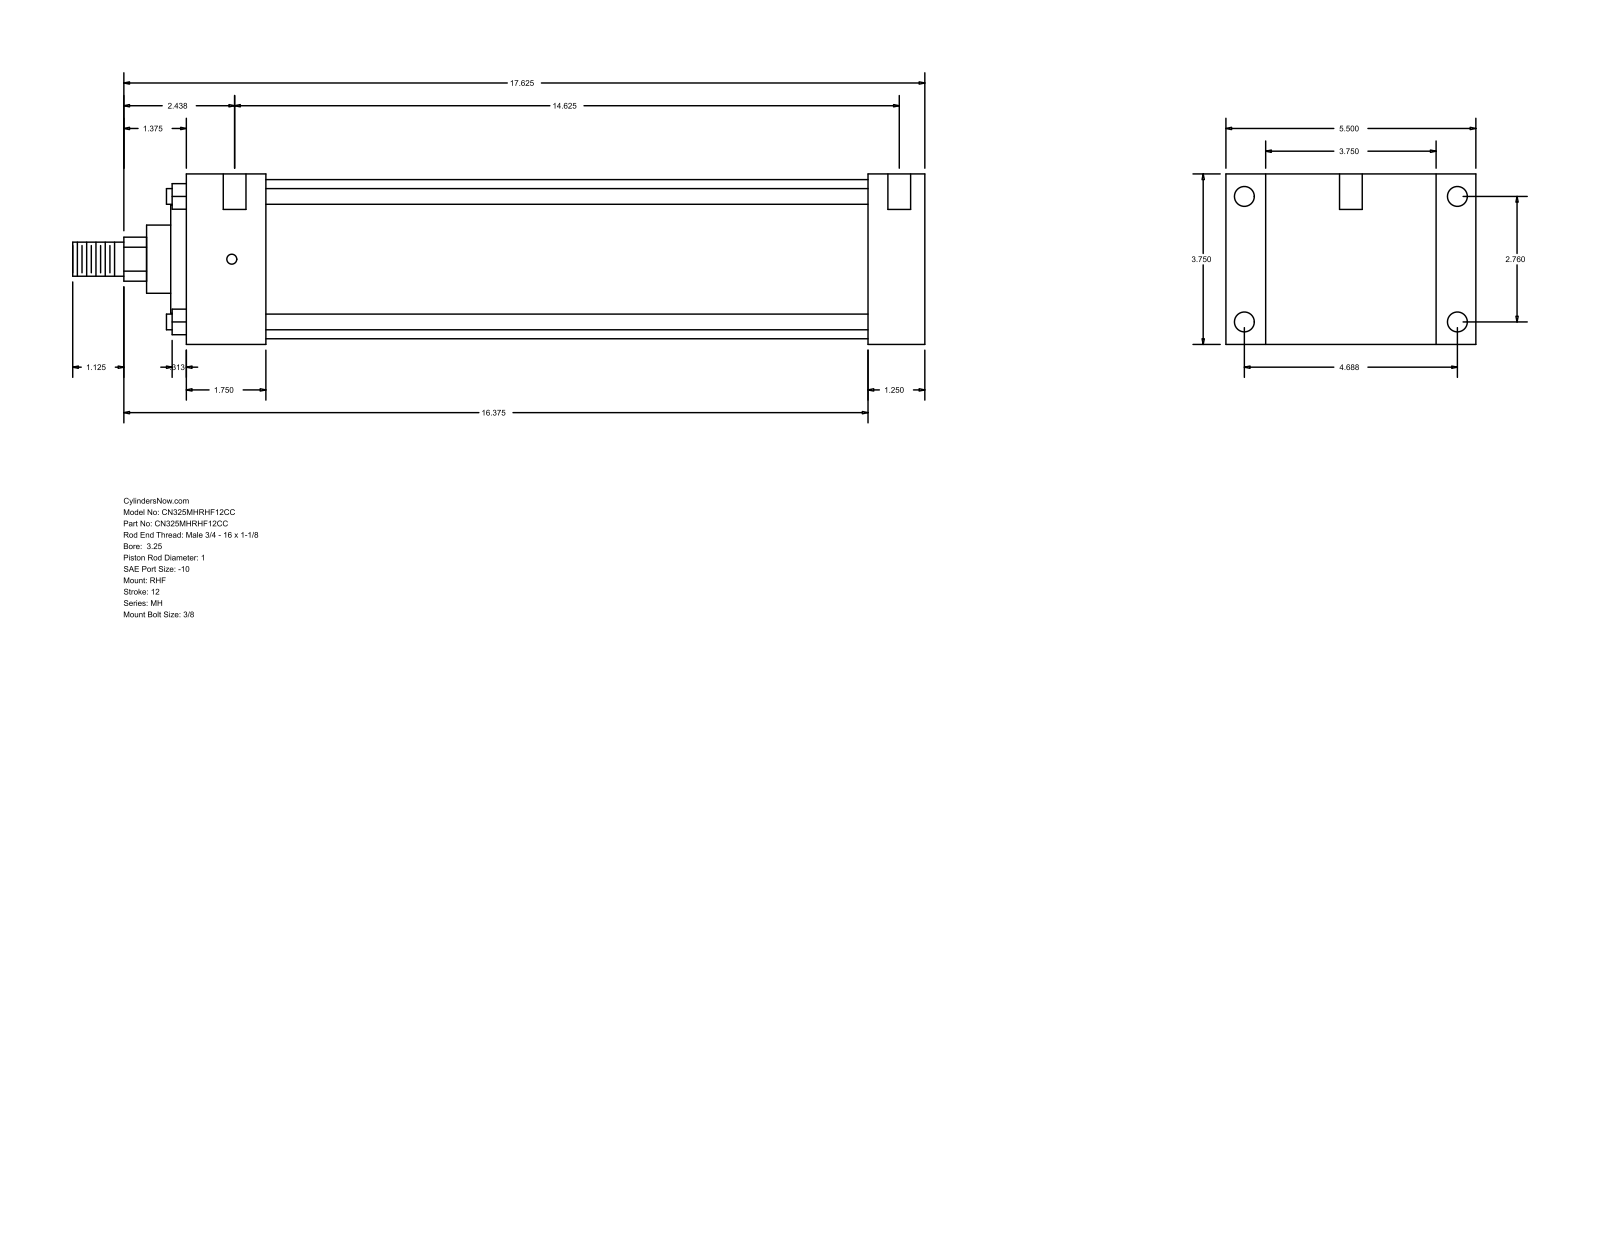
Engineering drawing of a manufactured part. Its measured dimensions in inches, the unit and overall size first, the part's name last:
Units: inches
Overall size (bounding box): 18.75 × 5.5 × 3.75
Round holes (diameter × count): ⌀0.219 ×4, ⌀0.438 ×4, ⌀0.5 ×2
Round bosses / shafts (diameter × count): ⌀0.345 ×4, ⌀3.5 ×1, ⌀2.375 ×1, ⌀1.5 ×1, ⌀1 ×1, ⌀0.75 ×1
Partial cylindrical surfaces — rounded edges, fillets, slot ends (radius × count): R0.484 ×1
Main face-to-face distances: 3.75, 1.25, 0.875, 4.625, 15, 16.25, 5.5, 1.75, 13.25, 14.5
Hole centre spacings: 2.76, 4.687, 5.439, 14.875, 0.062, 0.187, 14.625, 14.687
Bodies: 0 solids, 90 faces (61 planar, 29 cylindrical, 0 other)
Part name (STEP PRODUCT): MH_RHF__0325_1
STEP written by: GSSL Pune (CONFIG_CONTROL_DESIGN)
